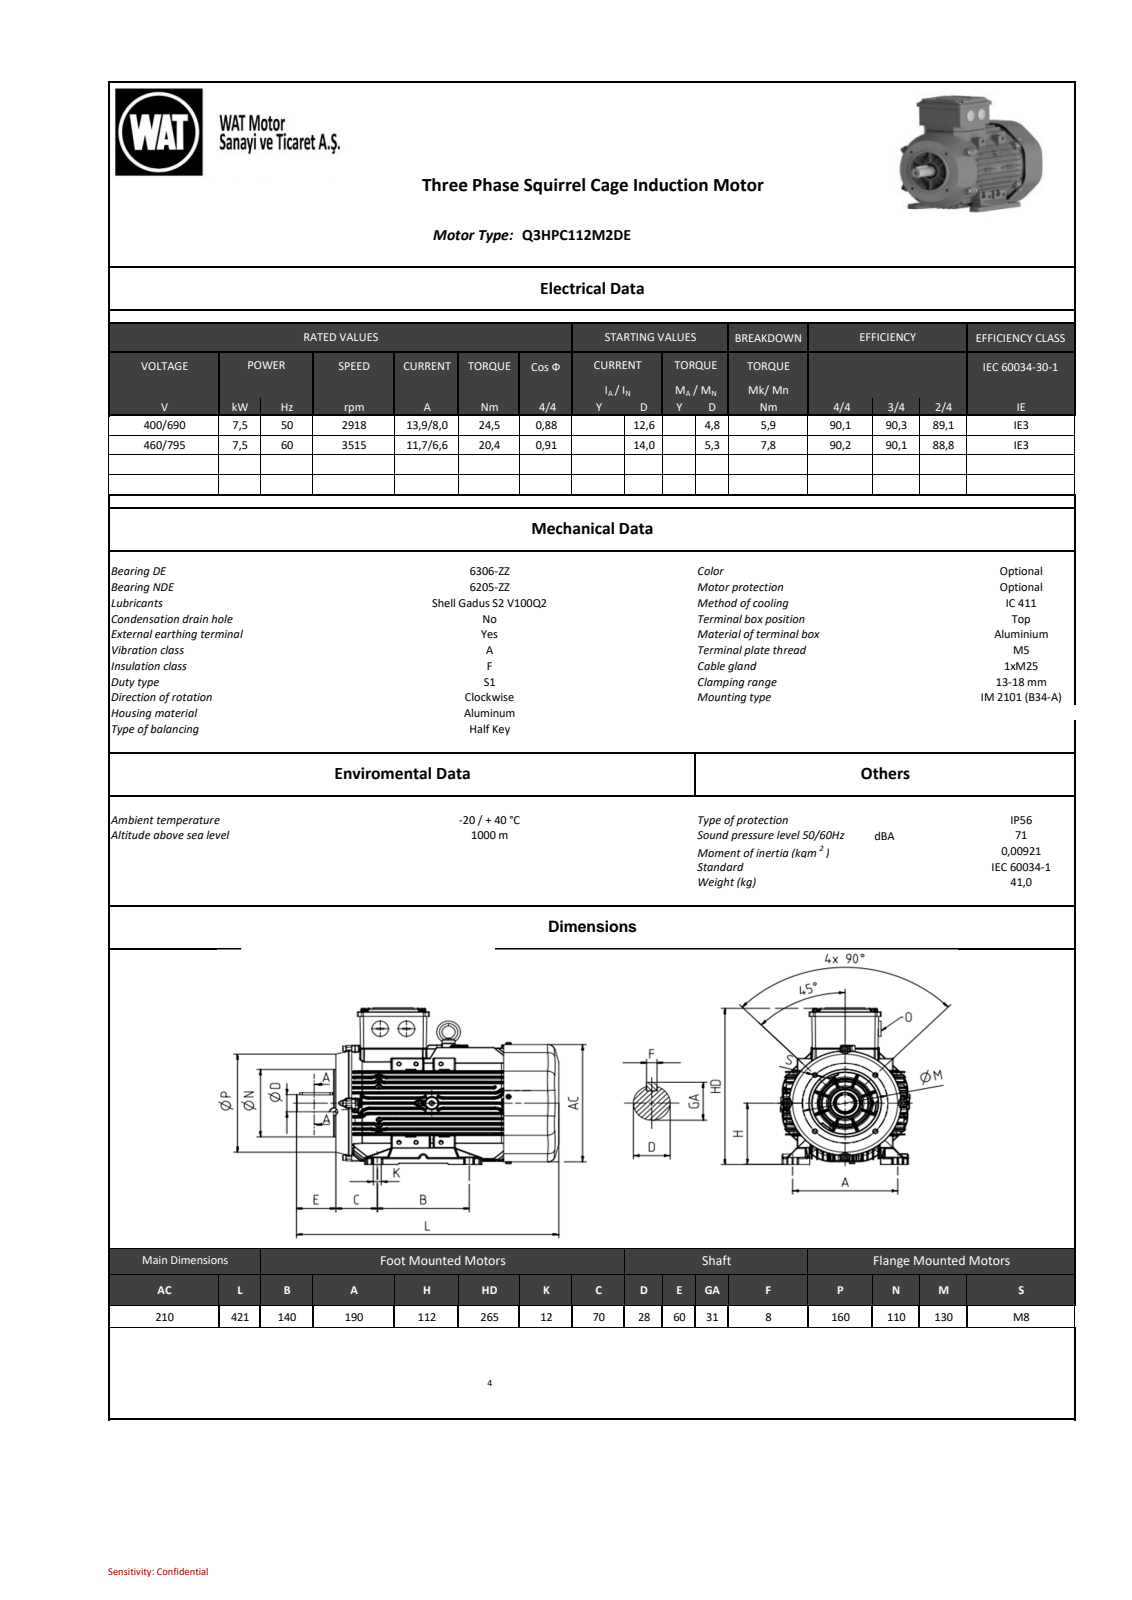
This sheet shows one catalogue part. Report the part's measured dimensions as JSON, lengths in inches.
{"part_name": "QH series_ 112_B34a _DEEP COVER__stp_objects", "step_written_by": "SIEMENS PLM Software NX2206.8101 (AUTOMOTIVE_DESIGN)", "units": "inches", "bodies": {"solids": 0, "faces": 7557, "planar": 1671, "cylindrical": 2898, "other": 2988}, "overall_size": [16.575, 10.845, 8.863], "round_holes": [[0.13, 2], [0.138, 2], [0.181, 2], [0.197, 2], [0.315, 1], [0.335, 1], [1.85, 1], [3.071, 1]], "round_bosses_or_shafts": [[0.315, 5], [0.512, 3], [0.394, 3], [0.984, 2], [0.236, 2], [7.402, 1], [4.331, 1], [1.411, 1]], "partial_cylinders_radius": [[0.079, 690], [0.031, 525], [0.039, 435], [0.02, 292], [0.047, 94], [0.118, 70], [0.157, 12], [0.236, 12]], "face_to_face_distances": [0.039, 0.846, 0.433, 1.416, 3.919, 0.983, 0.321, 4.444, 3.538, 3.56], "hole_center_spacings": [3.465, 3.487, 5.945]}
